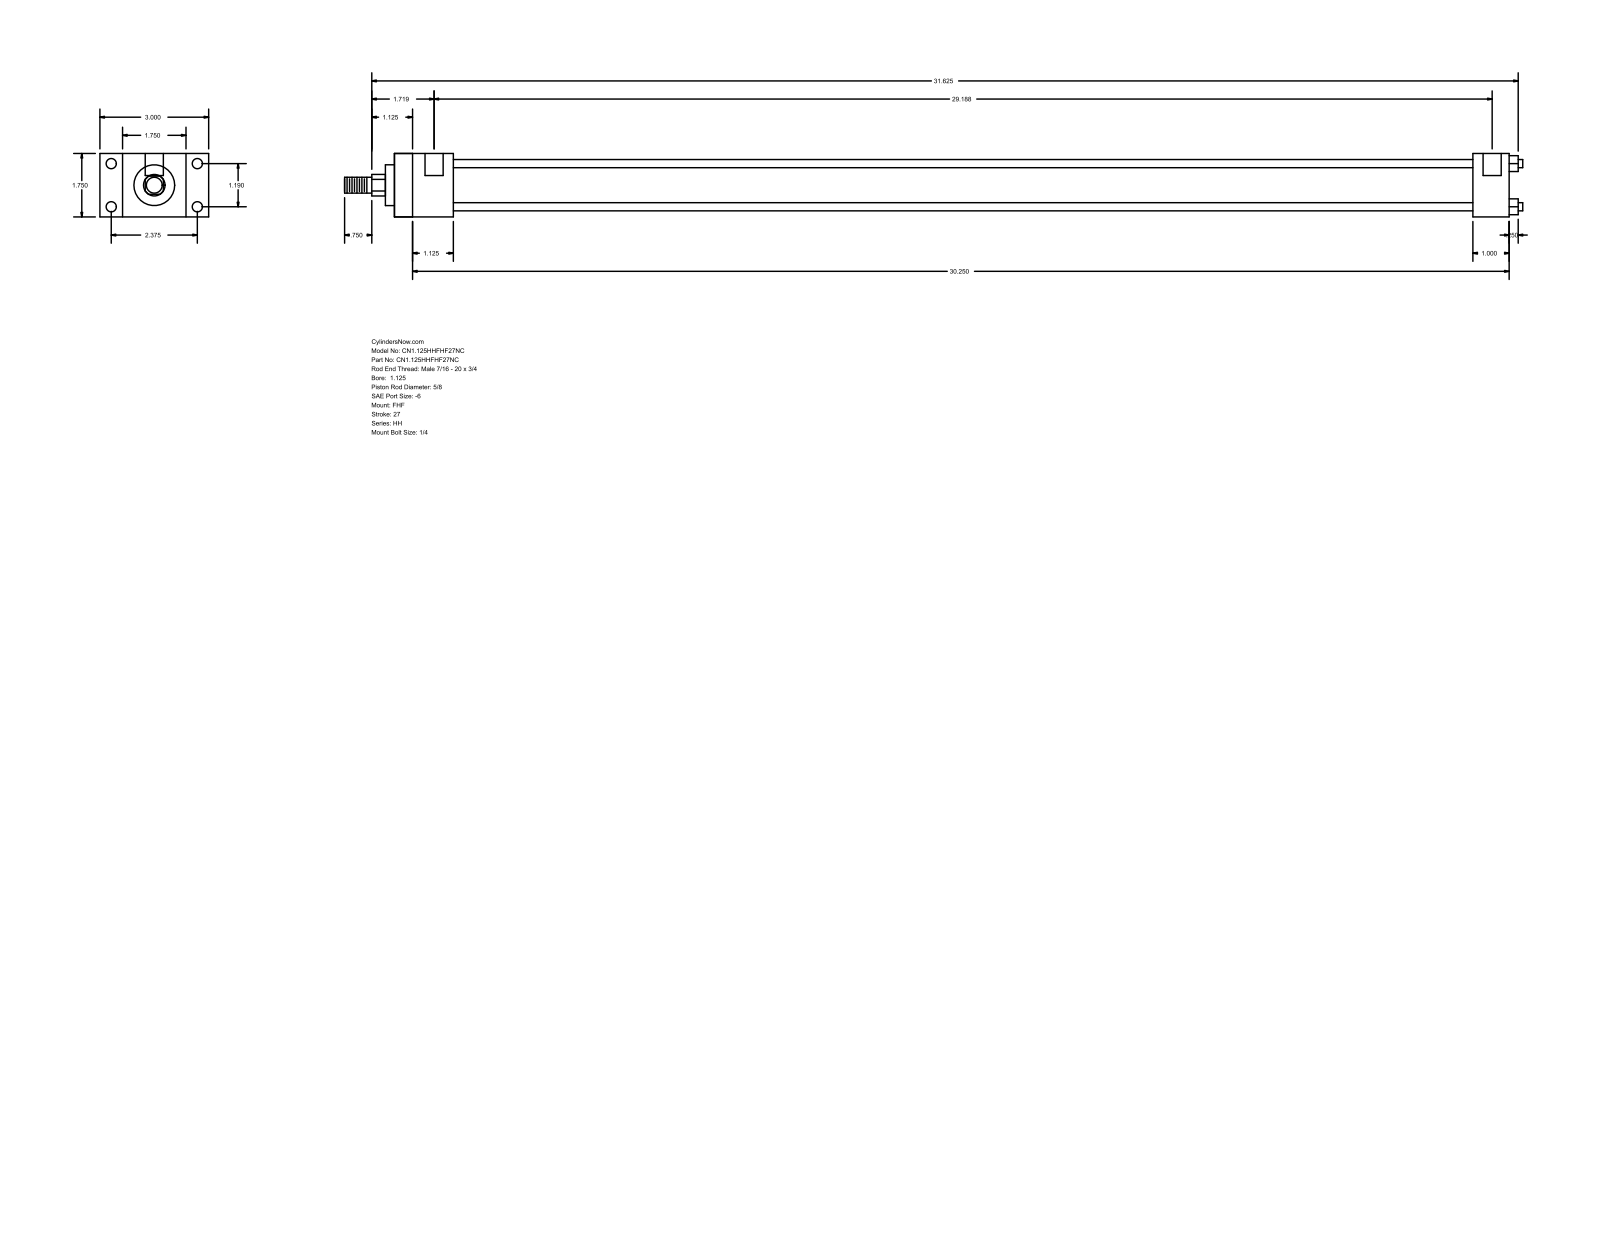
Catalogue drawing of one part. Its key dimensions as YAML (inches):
part_name: "HH_FHF__0112_0.625"
step_written_by: "GSSL Pune (CONFIG_CONTROL_DESIGN)"
units: inches
bodies: {solids: 0, faces: 88, planar: 60, cylindrical: 28, other: 0}
overall_size: [32.5, 3, 1.75]
round_holes:
  - {diameter: 0.219, count: 4}
  - {diameter: 0.281, count: 4}
  - {diameter: 0.5, count: 2}
round_bosses_or_shafts:
  - {diameter: 0.225, count: 4}
  - {diameter: 1.375, count: 1}
  - {diameter: 1.125, count: 1}
  - {diameter: 0.625, count: 1}
  - {diameter: 0.437, count: 1}
partial_cylinders:
  - {radius: 0.297, count: 1}
face_to_face_distances: [1.75, 0.625, 2.375, 1.625, 3, 30.75, 29.125, 1, 29.75, 28.125]
hole_center_spacings: [1.19, 2.375, 2.656, 29.063, 0.125, 29.187]
